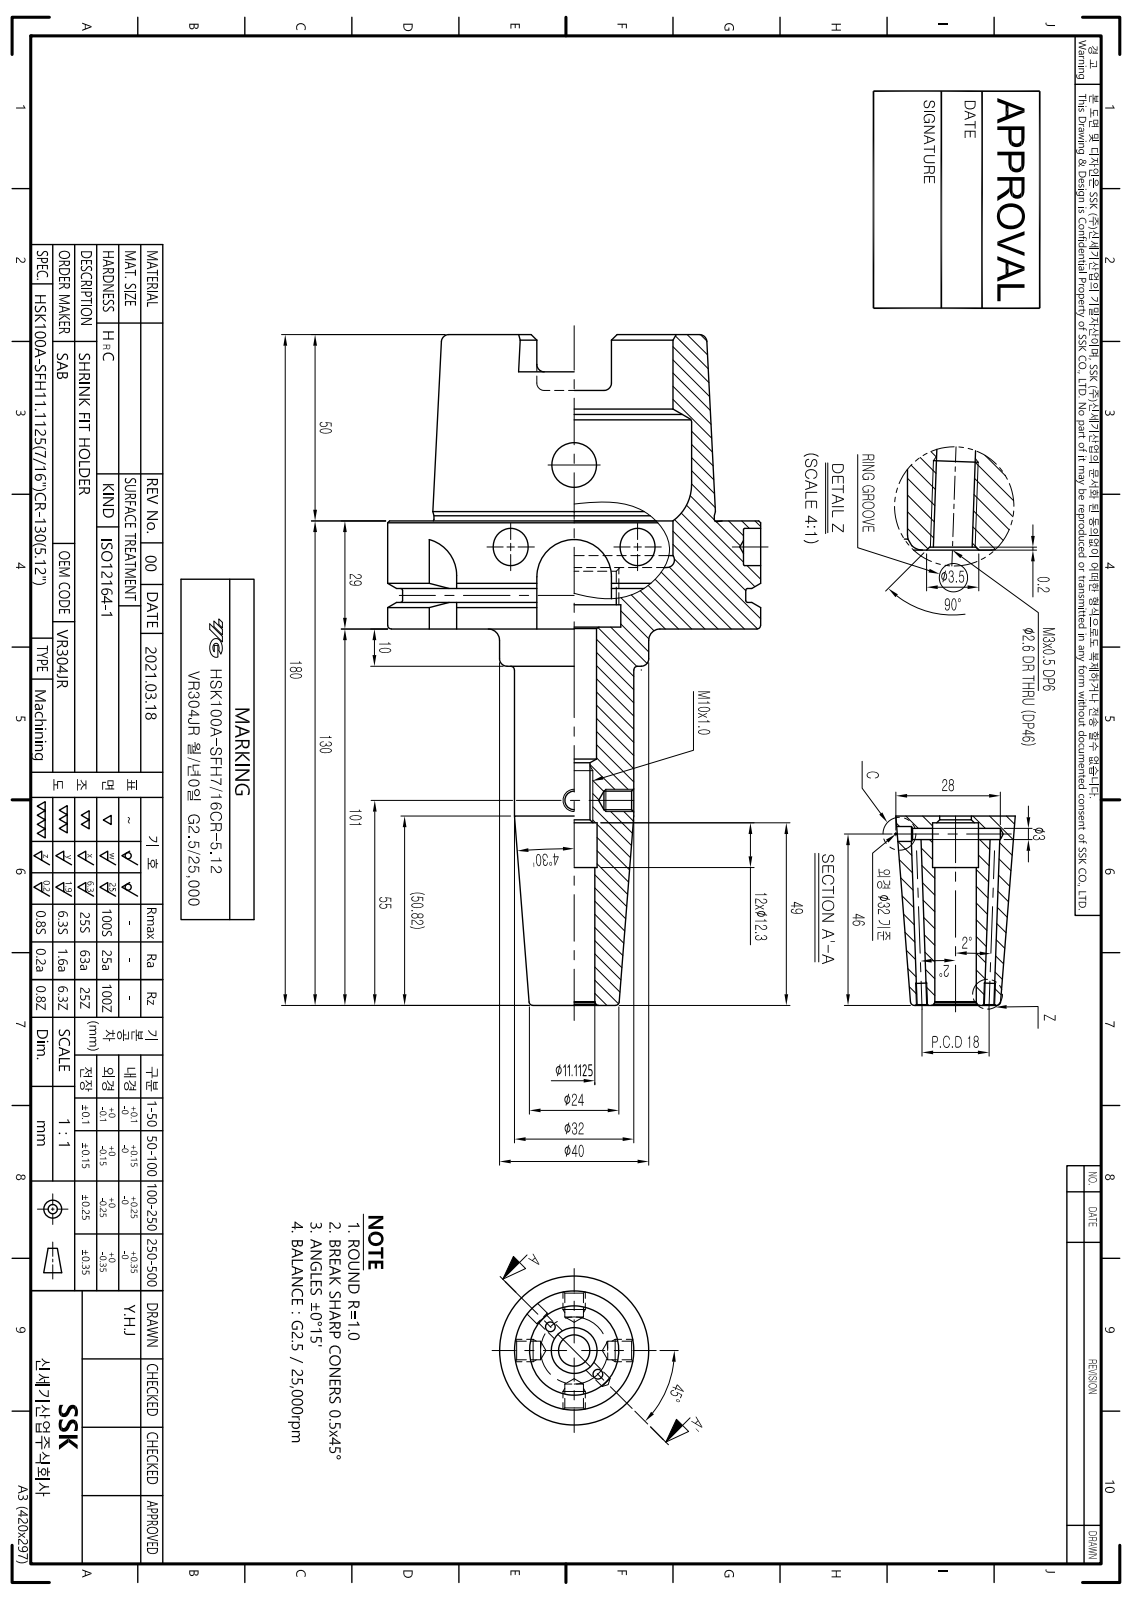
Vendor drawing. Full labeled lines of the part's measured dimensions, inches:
Part name (STEP PRODUCT): LO-HSK100A-SFH11.1125CR-130
STEP written by: Autodesk Inventor 2022 (AUTOMOTIVE_DESIGN)
Units: inches
Bodies: 1 solid, 123 faces (39 planar, 38 cylindrical, 46 other)
Overall size (bounding box): 7.087 × 3.937 × 3.937
Volume: 19.54 in³ · Surface area: 97.59 in²
Round holes (diameter × count): ⌀0.097 ×2, ⌀0.472 ×2, ⌀0.351 ×1, ⌀0.394 ×1, ⌀0.437 ×1, ⌀0.485 ×1, ⌀0.881 ×1, ⌀0.984 ×1, ⌀2.087 ×1, ⌀2.48 ×1
Round bosses / shafts (diameter × count): ⌀3.937 ×1, ⌀3.622 ×1, ⌀2.969 ×1, ⌀1.575 ×1, ⌀1.26 ×1
Partial cylindrical surfaces — rounded edges, fillets, slot ends (radius × count): R0.079 ×6, R0.192 ×4, R0.394 ×4
Main face-to-face distances: 1.142, 0.492, 0.65, 3.11, 2.461, 1.969, 3.465, 0.394, 3.091, 1.122
